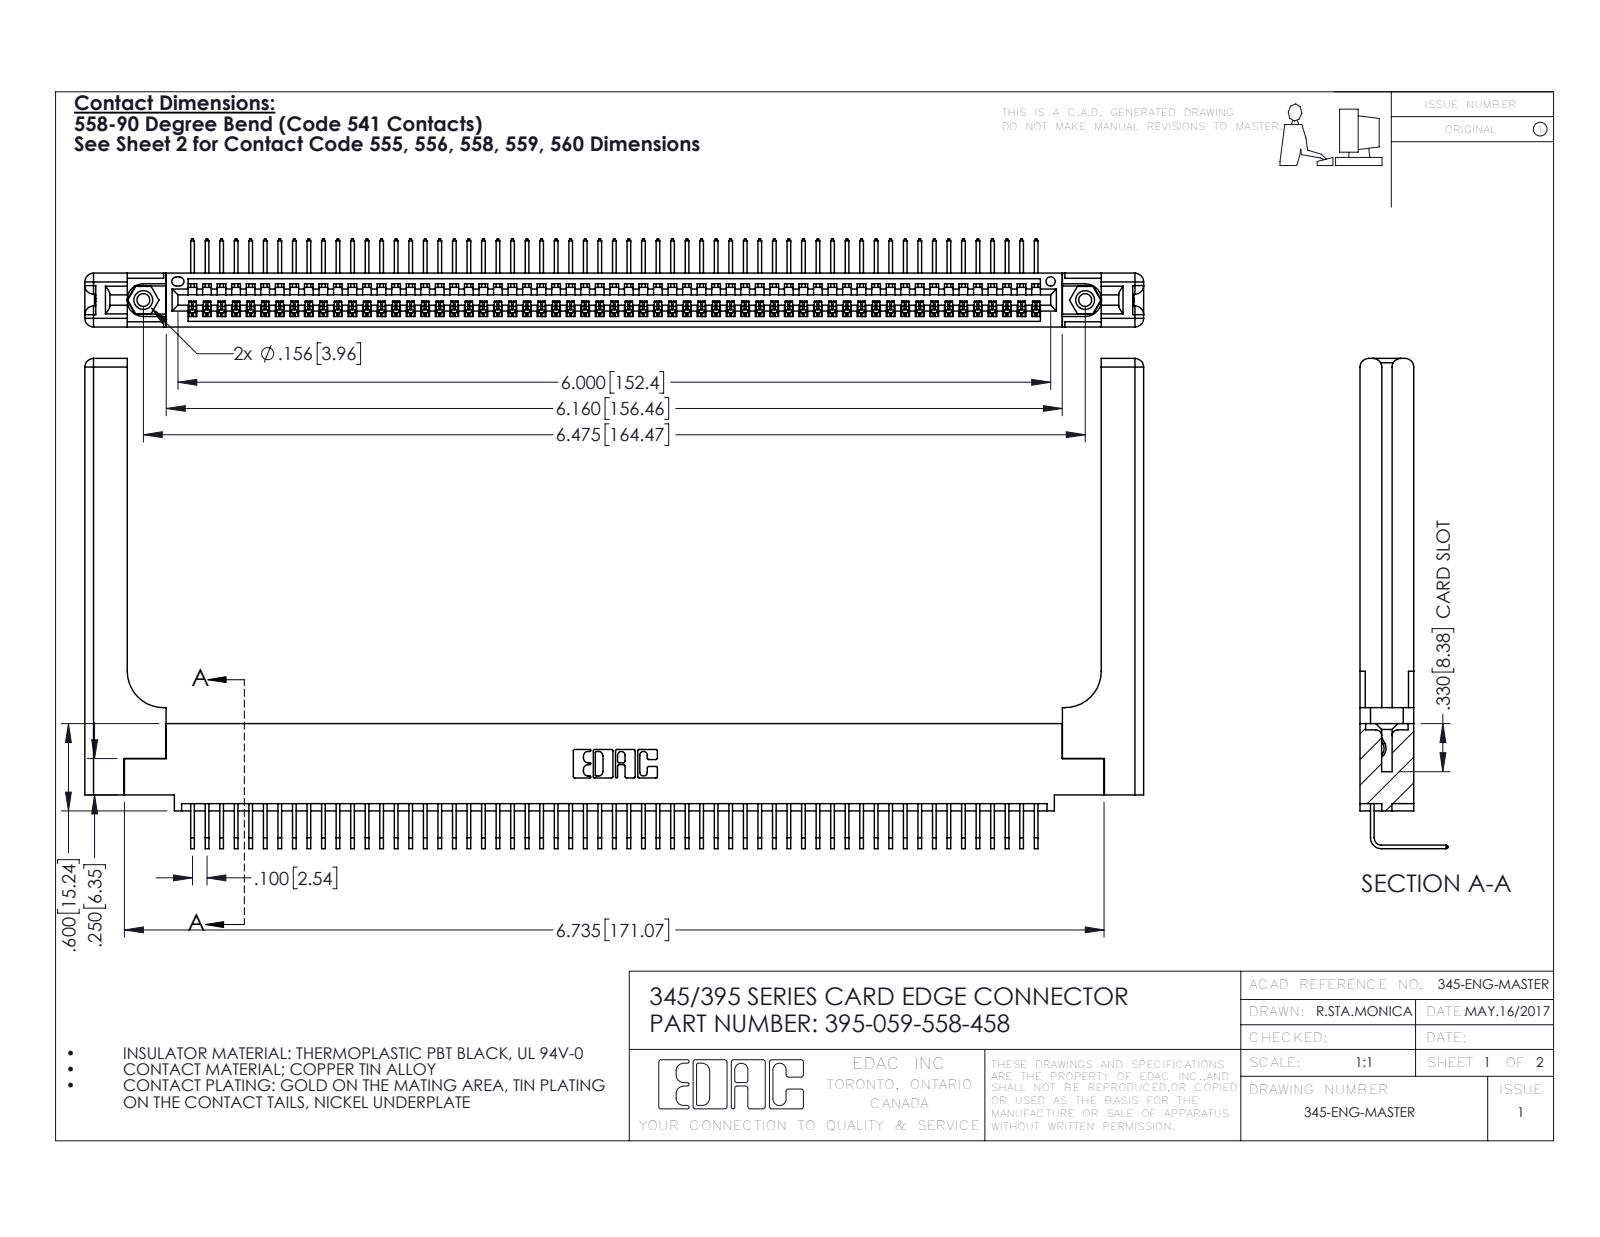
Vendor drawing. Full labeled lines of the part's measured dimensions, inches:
Part name (STEP PRODUCT): 345 Part_0.110 Offset - 0.156 Dia-TH; 345-292-001_558 Tail - 2; 345-250-001_345-250-001-102; 345-220-058_345-220-058 (+1 more)
STEP written by: SolidWorks 2016 (CONFIG_CONTROL_DESIGN)
Units: inches
Bodies: 64 solids, 3926 faces (2710 planar, 1156 cylindrical, 60 other)
Overall size (bounding box): 7.279 × 3.369 × 0.605
Volume: 1.607 in³ · Surface area: 47.21 in²
Round holes (diameter × count): ⌀0.089 ×2, ⌀0.125 ×2, ⌀0.156 ×2, ⌀0.064 ×1
Round bosses / shafts (diameter × count): ⌀0.155 ×2
Partial cylindrical surfaces — rounded edges, fillets, slot ends (radius × count): R0.006 ×118, R0.01 ×22, R0.06 ×16, R0.007 ×6, R0.031 ×6, R0.026 ×3, R0.03 ×2, R0.031 ×2
Main face-to-face distances: 0.072, 0.37, 0.298, 0.098, 0.272, 0.025, 0.2, 0.225, 0.148, 0.15
Hole centre spacings: 0.27, 6.239, 6.475
